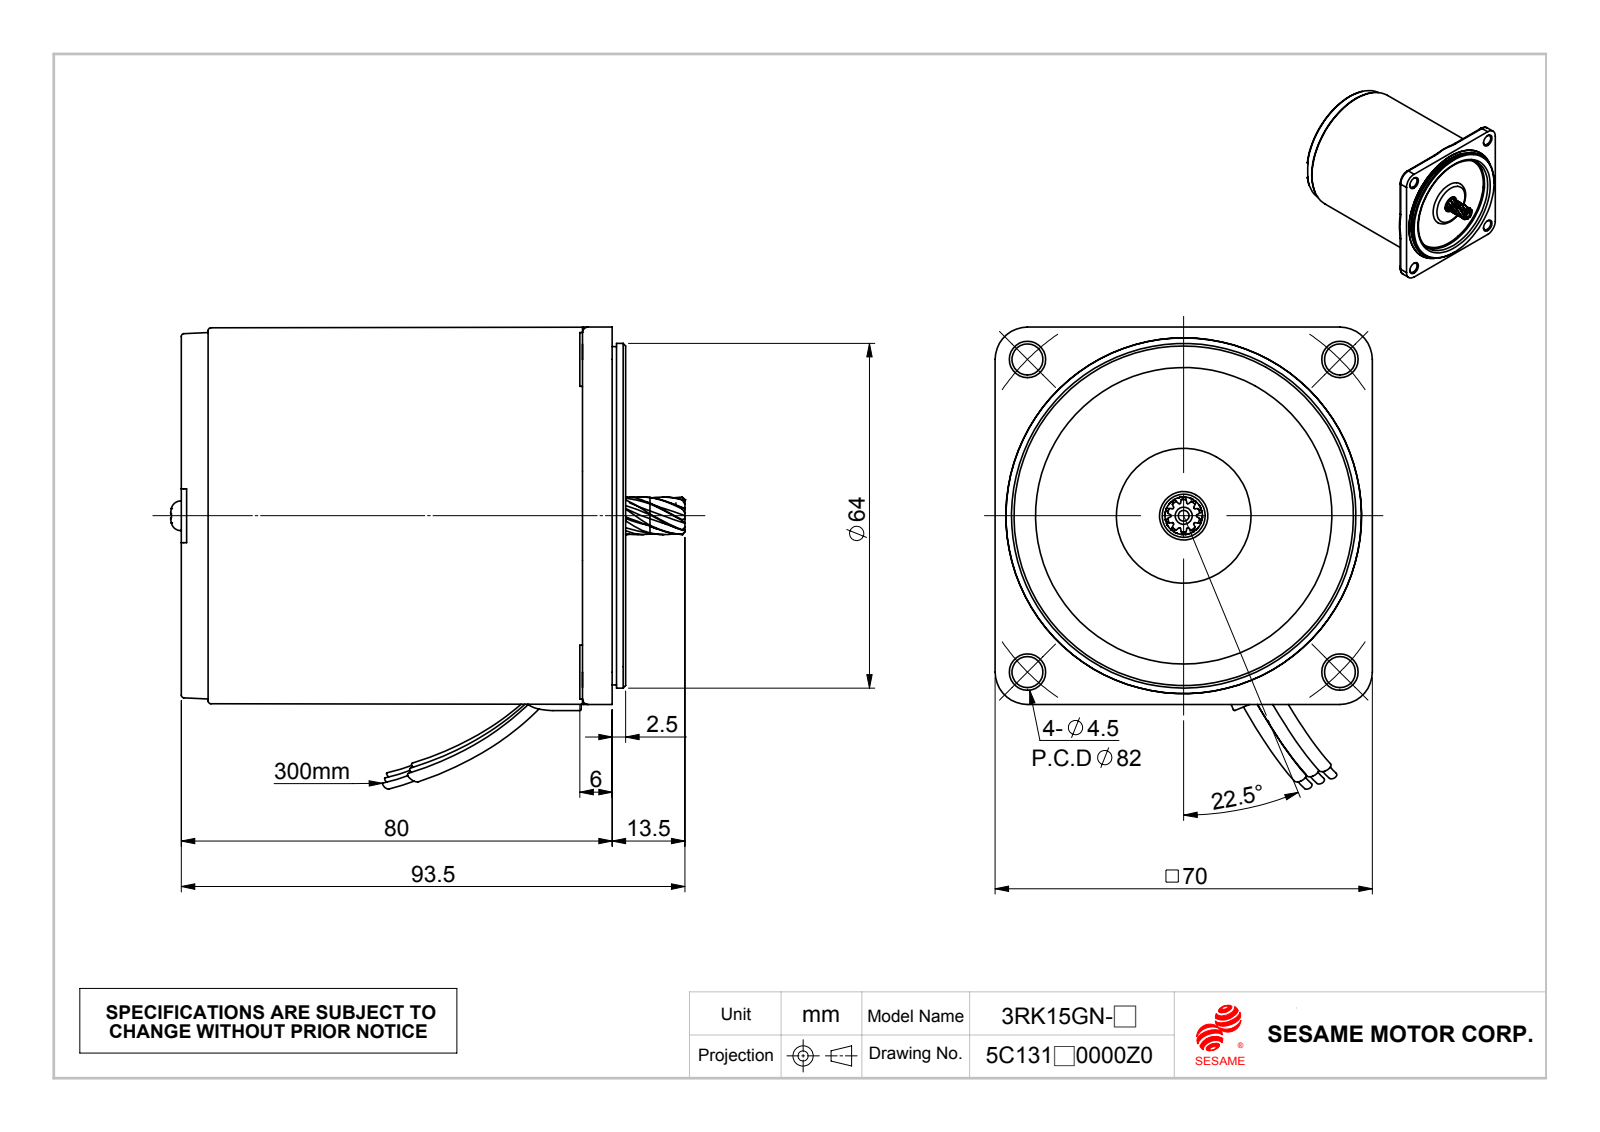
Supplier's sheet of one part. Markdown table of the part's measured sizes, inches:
| quantity | value |
| --- | --- |
| part name | 線扣; M315-RK_3.鑽孔; C364_車工(成品); 15GN_0.成品 (+1 more) |
| STEP written by | SolidWorks 2010 (CONFIG_CONTROL_DESIGN) |
| units | inches |
| bodies | 10 solids, 371 faces (107 planar, 107 cylindrical, 157 other) |
| overall size | 3.758 × 3.376 × 2.756 |
| volume | 19.1 in³ |
| surface area | 64.62 in² |
| round holes (diameter × count) | 0.226 × 4, 0.098 × 3, 0.157 × 2, 0.079 × 1, 0.283 × 1, 0.354 × 1, 0.374 × 1, 0.709 × 1, 2.165 × 1, 2.291 × 1, 2.598 × 1 |
| round bosses / shafts (diameter × count) | 0.394 × 4, 0.217 × 2, 0.118 × 2, 2.517 × 1, 2.47 × 1, 2.261 × 1, 2.252 × 1, 1.417 × 1 |
| partial cylindrical surfaces (radius × count) | 0.01 × 8, 0.012 × 8, 0.039 × 4, 0.236 × 4, 0.207 × 1, 1.335 × 1 |
| main face-to-face distances | 3.047, 3.051, 0.059, 2.988, 0.063, 0.059, 3.11, 0.122, 0.063, 3.091 |
| hole center spacings | 1.285, 1.615, 2.042, 2.283, 0.551, 3.229, 1.102 |
